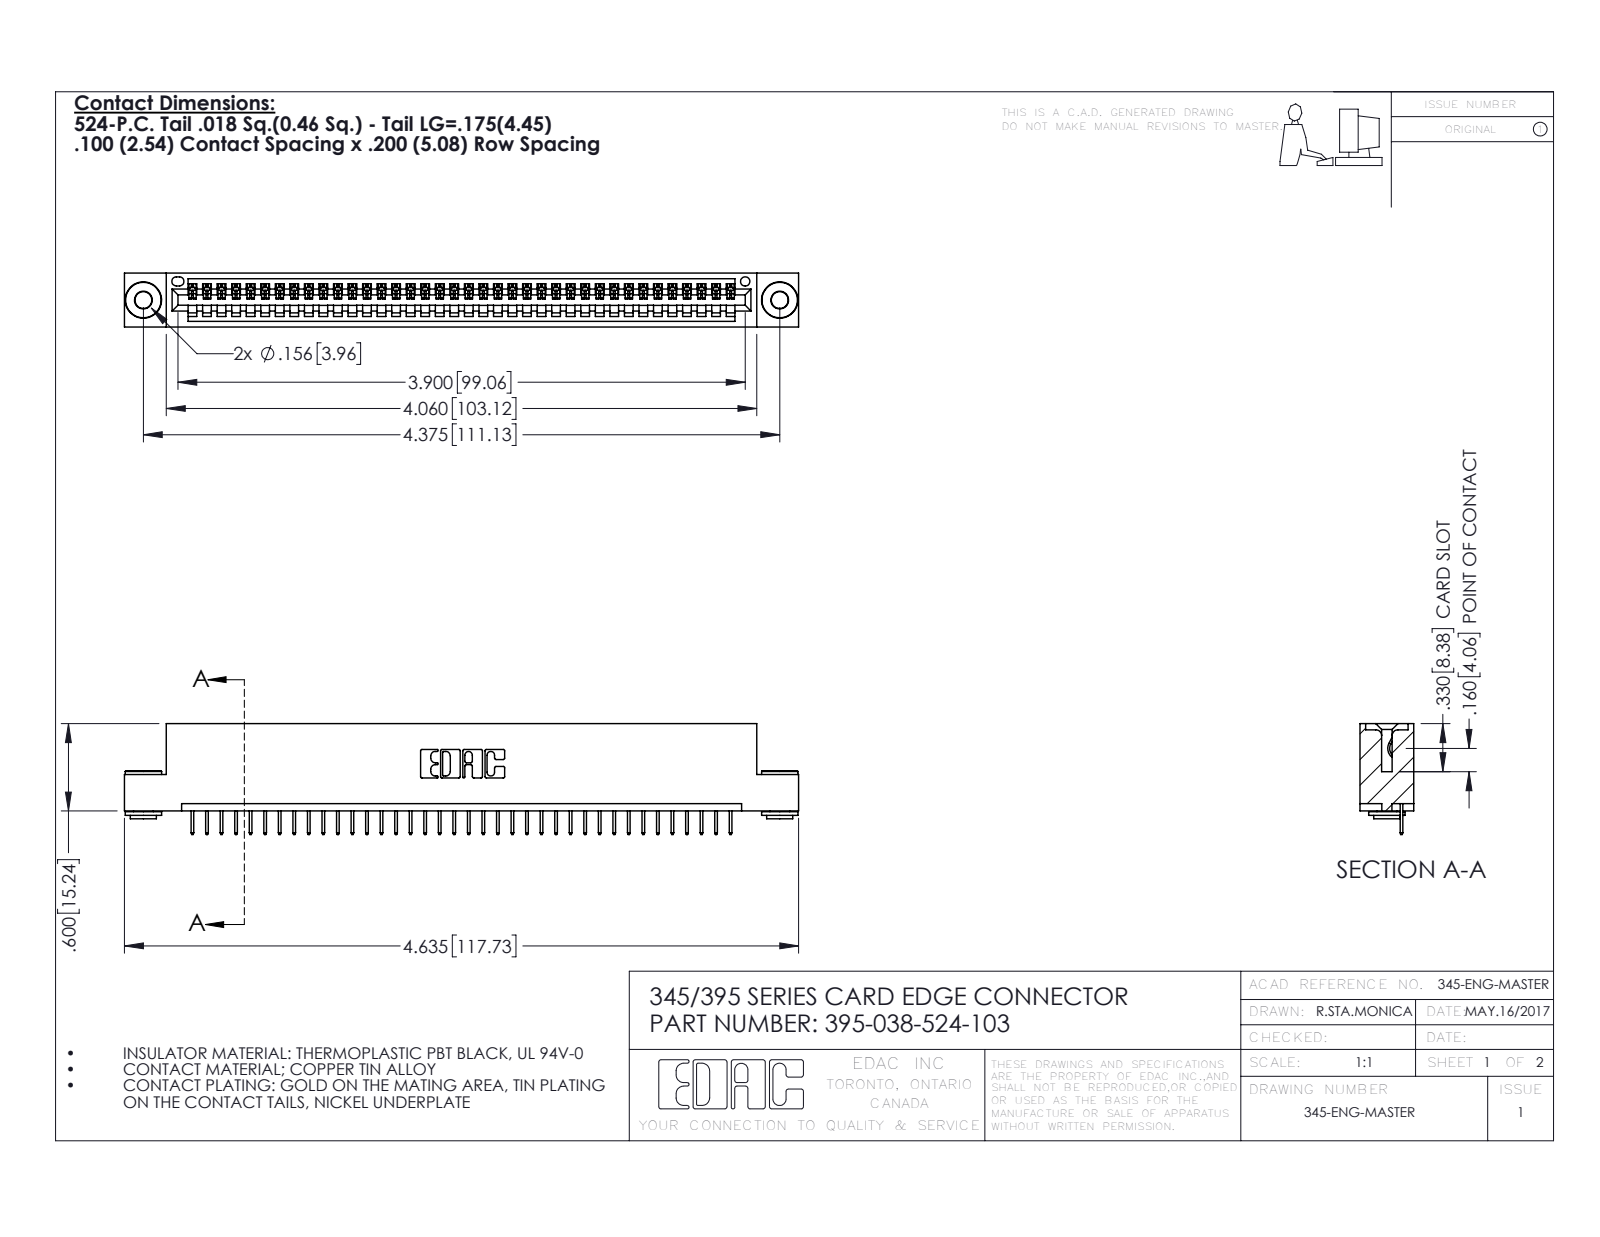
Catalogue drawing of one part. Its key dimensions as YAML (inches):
part_name: "345-292-001_345-293-124; 345-250-002_345-250-002-102; 395-038-524-103; 345 Part_Flush Mounting Lugs - 0.156 Dia-TH"
step_written_by: "SolidWorks 2016 (CONFIG_CONTROL_DESIGN)"
units: inches
bodies: {solids: 41, faces: 2520, planar: 1838, cylindrical: 674, other: 8}
overall_size: [4.635, 0.762, 0.37]
volume: 0.672
surface_area: 22.2
round_holes:
  - {diameter: 0.116, count: 2}
  - {diameter: 0.156, count: 2}
  - {diameter: 0.064, count: 1}
round_bosses_or_shafts:
  - {diameter: 0.25, count: 2}
  - {diameter: 0.18, count: 2}
  - {diameter: 0.136, count: 2}
partial_cylinders:
  - {radius: 0.006, count: 76}
  - {radius: 0.01, count: 22}
  - {radius: 0.007, count: 6}
  - {radius: 0.031, count: 6}
  - {radius: 0.026, count: 3}
  - {radius: 0.031, count: 2}
  - {radius: 0.04, count: 2}
  - {radius: 0.014, count: 1}
face_to_face_distances: [0.072, 0.298, 0.37, 0.2, 0.025, 0.098, 0.272, 0.225, 0.072, 0.149]
hole_center_spacings: [0.27, 4.139, 4.375]
